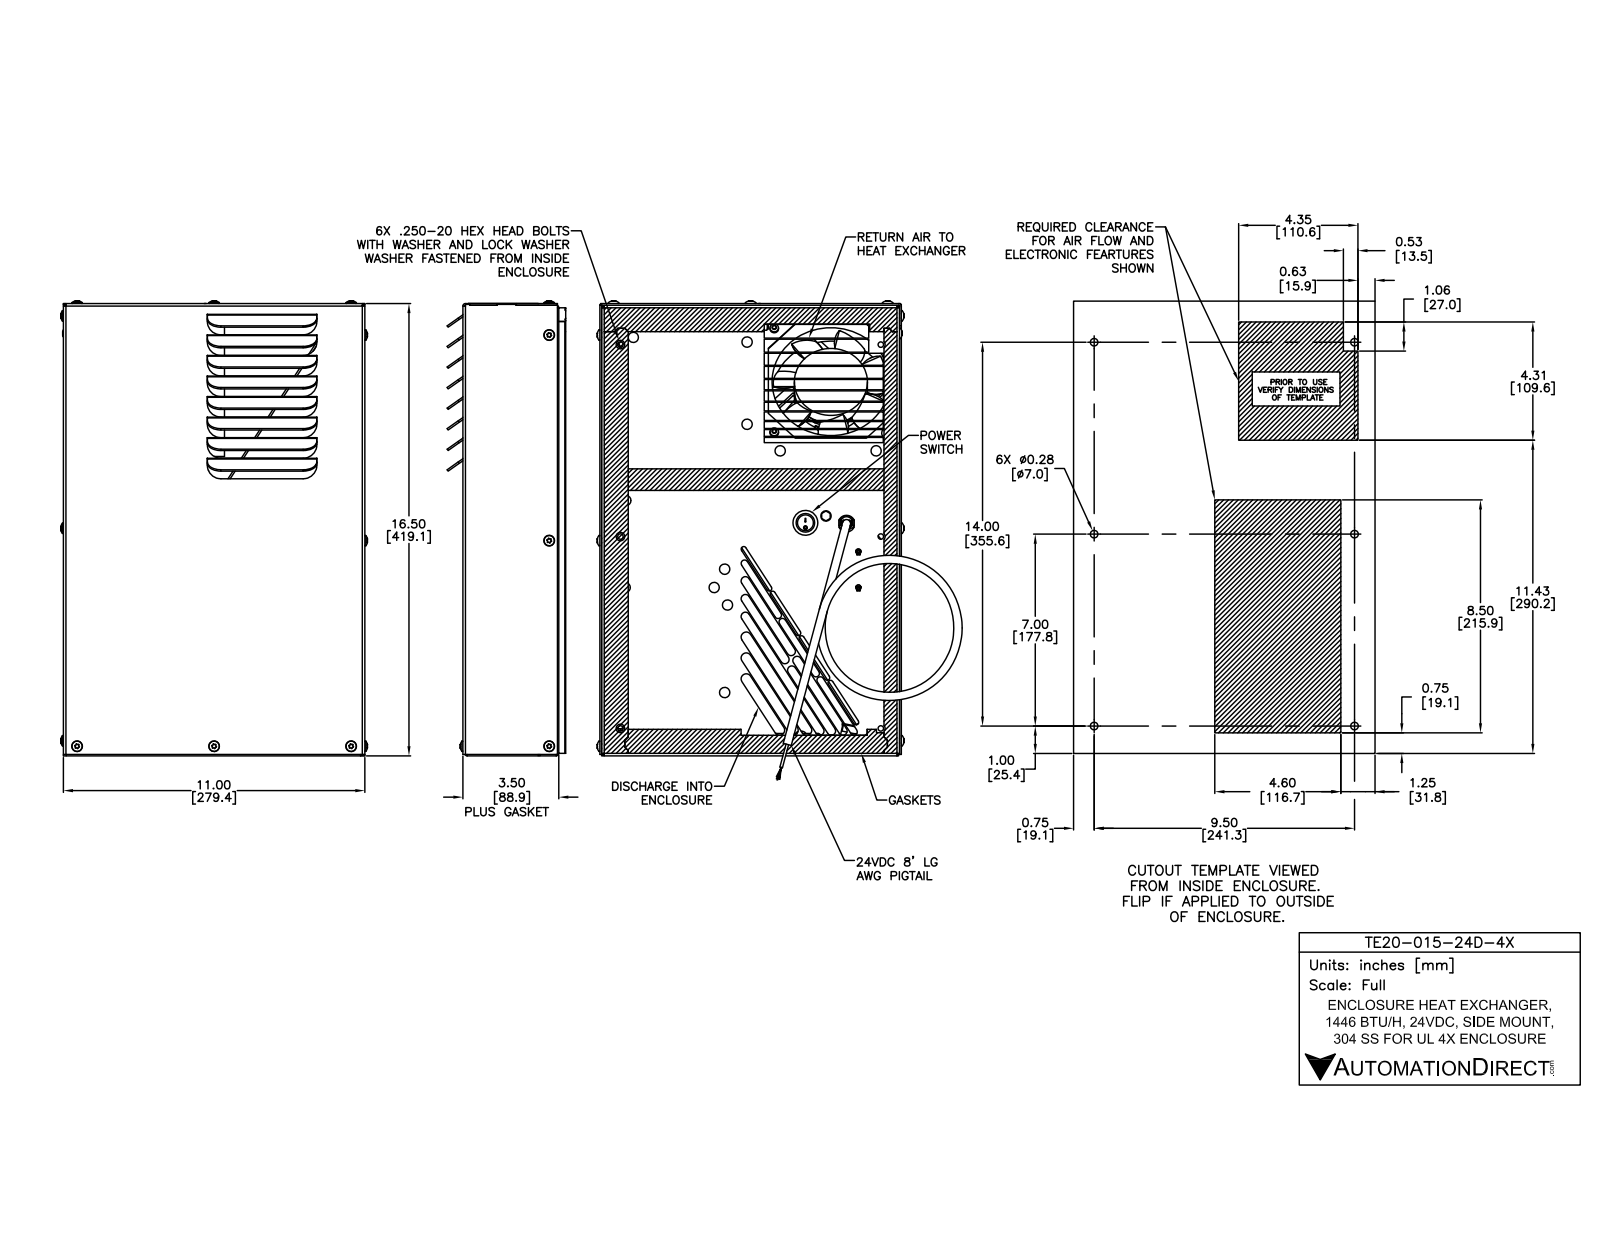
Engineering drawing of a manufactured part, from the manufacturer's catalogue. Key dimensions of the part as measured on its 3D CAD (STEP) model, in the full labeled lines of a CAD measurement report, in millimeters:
Part name (STEP PRODUCT): TE20-015-24D-4X
STEP written by: SolidWorks 2017 (AUTOMOTIVE_DESIGN)
Units: millimetres
Bodies: 66 solids, 2808 faces (1639 planar, 897 cylindrical, 272 other)
Overall size (bounding box): 449.5 × 339.1 × 191.1
Volume: 2 283 000 mm³ · Surface area: 1 544 000 mm²
Round holes (diameter × count): ⌀4.9 ×21, ⌀5.6 ×20, ⌀5.2 ×11, ⌀3.5 ×8, ⌀4.1 ×8, ⌀4.5 ×8, ⌀12.7 ×8, ⌀2.8 ×6, ⌀5.1 ×6, ⌀4 ×4, ⌀5.4 ×4, ⌀7.9 ×3
Round bosses / shafts (diameter × count): ⌀9.3 ×13, ⌀4.3 ×13, ⌀8 ×8, ⌀7.9 ×8, ⌀4.7 ×8, ⌀4.2 ×8, ⌀3.3 ×8, ⌀8.3 ×6
Partial cylindrical surfaces — rounded edges, fillets, slot ends (radius × count): R0.5 ×79, R0.5 ×78, R0.8 ×54, R2.4 ×48, R0.6 ×38, R1.5 ×28, R0.8 ×18, R0.6 ×16
Main face-to-face distances: 1.6, 87.3, 1.6, 85.8, 88.9, 276.1, 277.7, 6.4, 1.7, 95.3
Hole centre spacings: 105, 31.8, 148.5, 74.2, 148.5, 105, 74.2, 28.6
